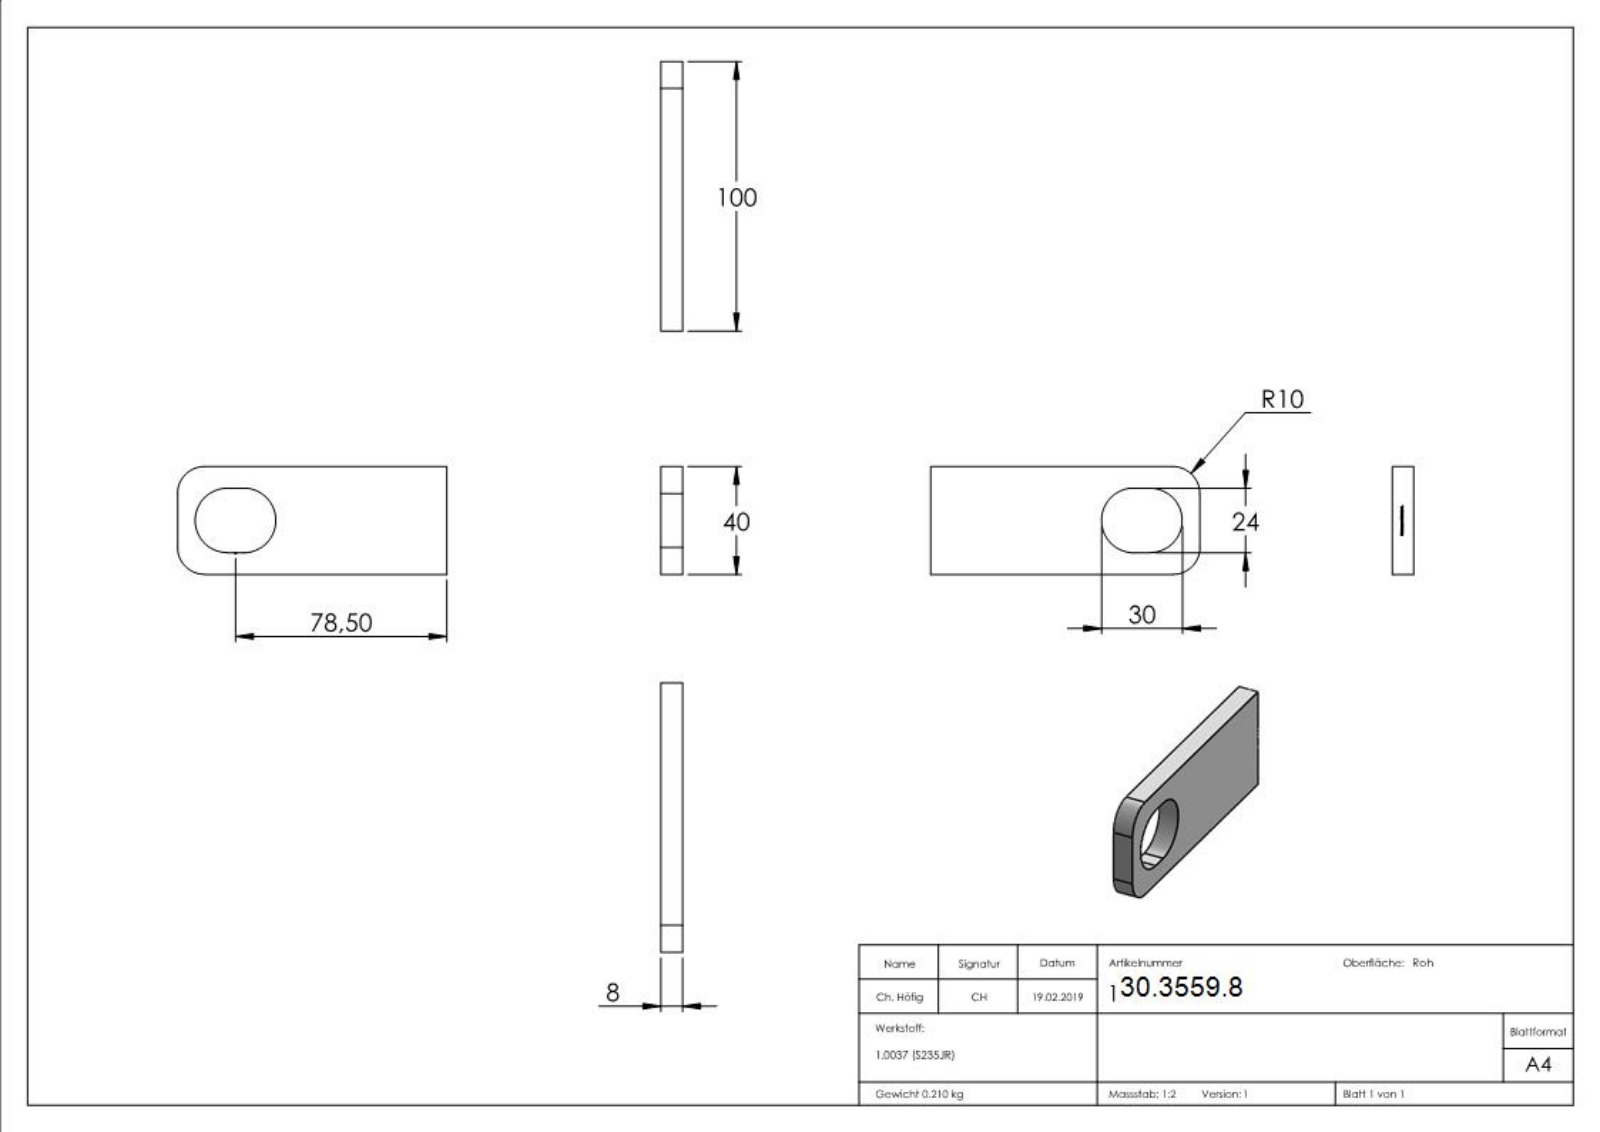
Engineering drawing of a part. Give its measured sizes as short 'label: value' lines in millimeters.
name: 120-M24-L
written by: SolidWorks 2015 (CONFIG_CONTROL_DESIGN)
unit: mm
bodies: 1 solid, 216 faces (142 planar, 5 cylindrical, 69 other)
size: 100 × 40 × 8
volume: 26 885 mm³; area: 9 597 mm²
rounds: 2× R10, 2× R12
face distances: 8, 40, 100, 32, 24, 99.9, 4, 10.44, 0.67, 3.74
